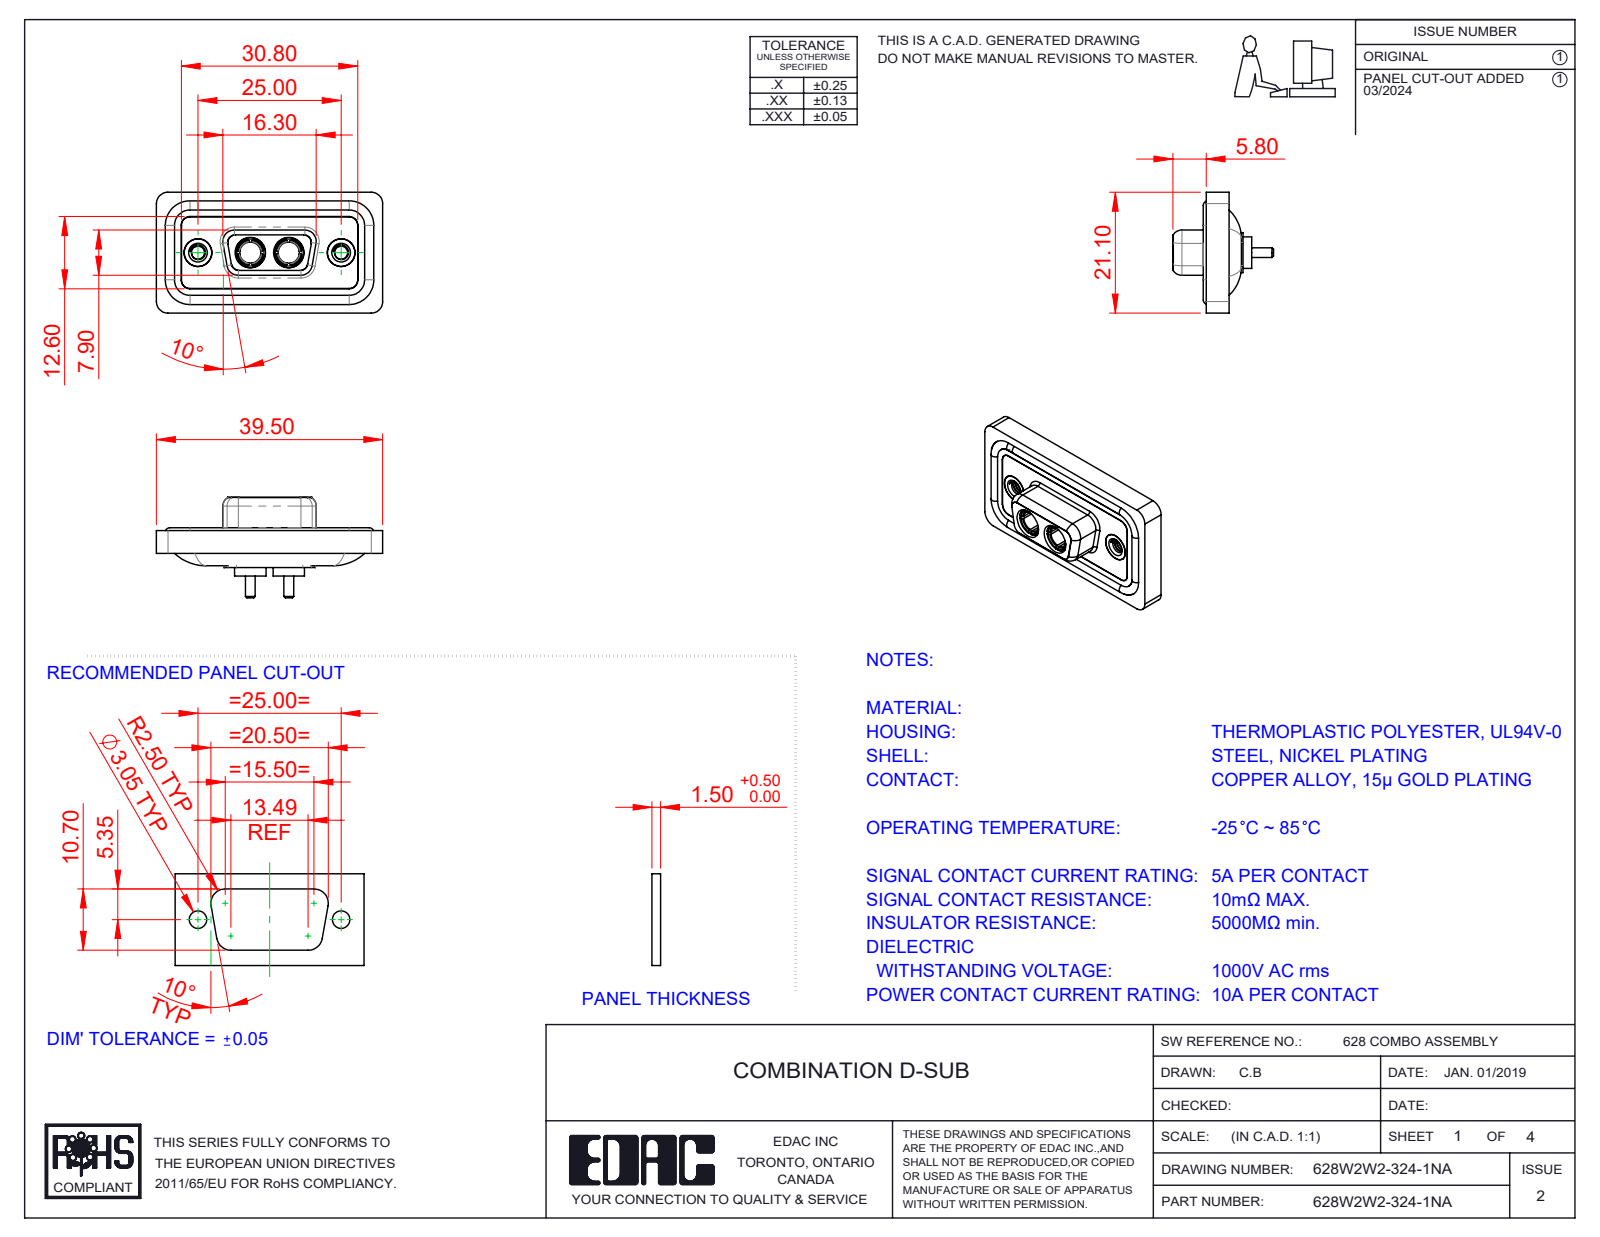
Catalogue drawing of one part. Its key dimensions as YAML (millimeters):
part_name: "628W2W2-324-1NA; 628Combo Waterproof Housing_09 Contacts; Power Socket_10A S; 628Combo Shell Front_09 Contacts (+3 more)"
step_written_by: "SolidWorks 2023 (CONFIG_CONTROL_DESIGN)"
units: millimeters
bodies: {solids: 11, faces: 532, planar: 163, cylindrical: 236, other: 133}
overall_size: [39.5, 21.1, 17.55]
volume: 4685
surface_area: 7608
round_holes:
  - {diameter: 4.85, count: 4}
  - {diameter: 2.26, count: 2}
  - {diameter: 3.7, count: 2}
  - {diameter: 4, count: 2}
  - {diameter: 4.05, count: 2}
  - {diameter: 5, count: 2}
  - {diameter: 5.3, count: 2}
round_bosses_or_shafts:
  - {diameter: 1.6, count: 4}
  - {diameter: 5.5, count: 2}
  - {diameter: 5.2, count: 2}
  - {diameter: 4.96, count: 2}
  - {diameter: 4.95, count: 2}
  - {diameter: 4.8, count: 2}
  - {diameter: 4.75, count: 2}
  - {diameter: 3.75, count: 2}
partial_cylinders:
  - {radius: 1.5, count: 22}
  - {radius: 2, count: 18}
  - {radius: 1.35, count: 8}
  - {radius: 1.6, count: 8}
  - {radius: 0.25, count: 4}
  - {radius: 0.5, count: 4}
  - {radius: 0.6, count: 4}
  - {radius: 0.65, count: 4}
face_to_face_distances: [0.4, 1.8, 1.1, 2.9, 0.5, 1.6, 5.65, 1.5, 7.45, 5.35]
hole_center_spacings: [9.14, 15.86, 6.72, 25]
